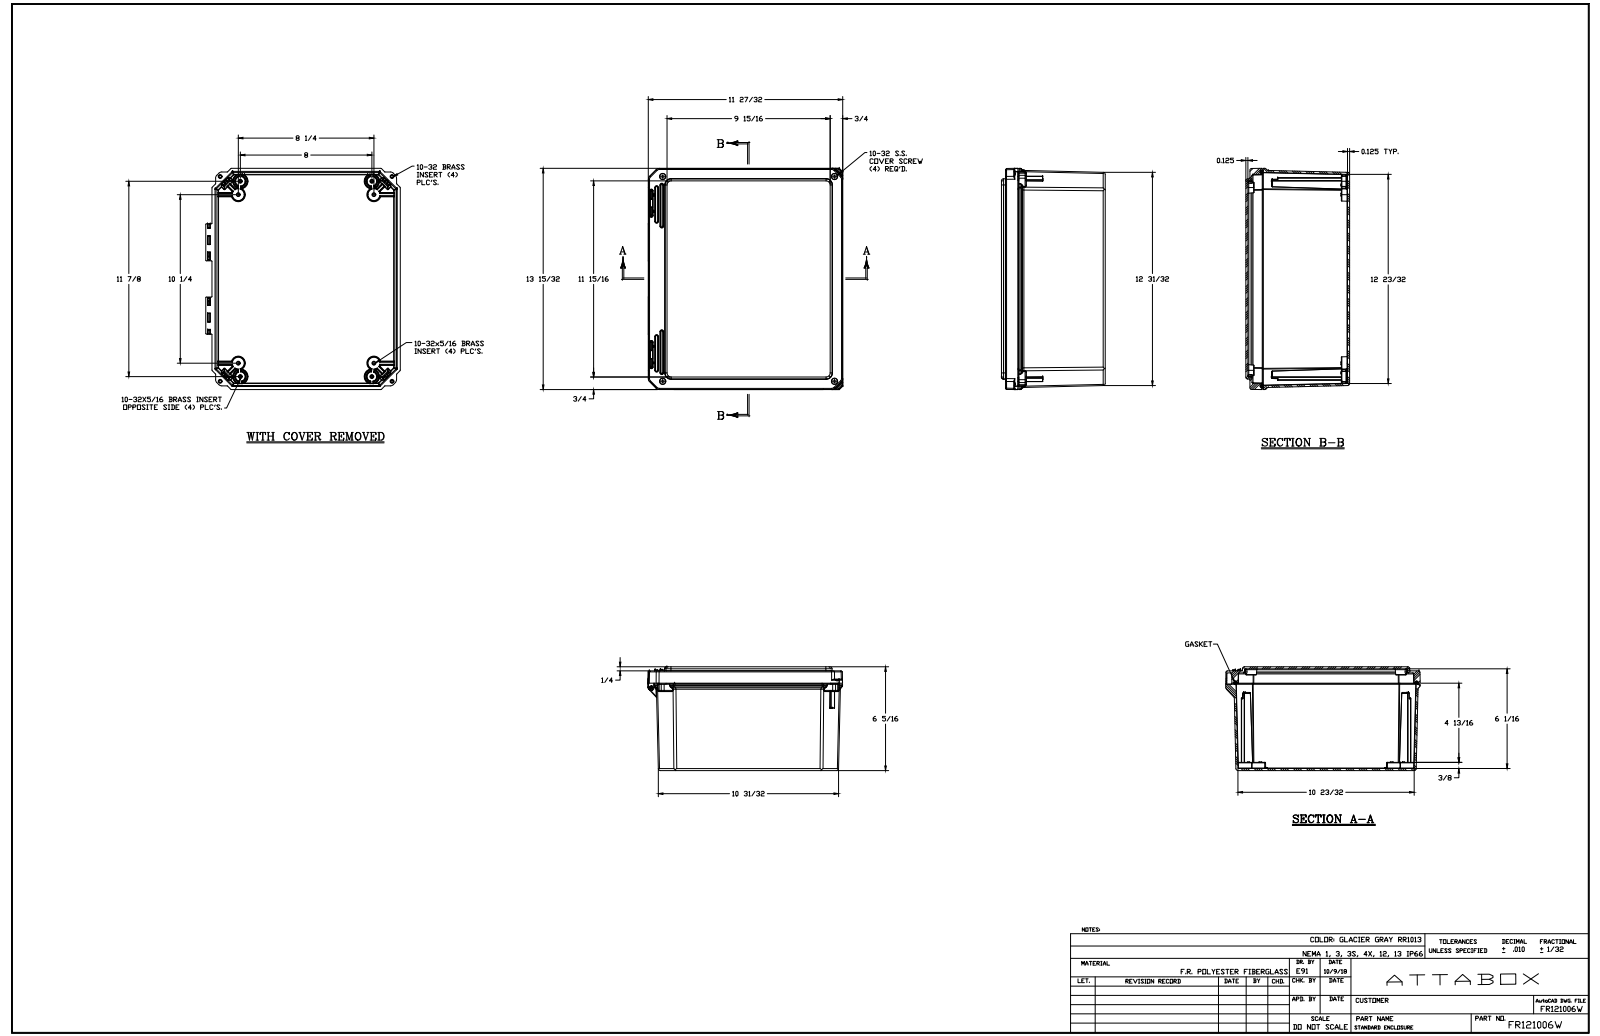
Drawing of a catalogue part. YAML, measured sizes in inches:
part_name: "FR121006W"
step_written_by: "SolidWorks 2018 (AUTOMOTIVE_DESIGN)"
units: inches
bodies: {solids: 27, faces: 2068, planar: 683, cylindrical: 758, other: 627}
overall_size: [13.46, 11.831, 6.31]
volume: 92.57
surface_area: 1268
round_holes:
  - {diameter: 0.156, count: 16}
  - {diameter: 0.152, count: 8}
  - {diameter: 0.252, count: 4}
  - {diameter: 0.253, count: 4}
  - {diameter: 0.219, count: 2}
  - {diameter: 0.227, count: 2}
  - {diameter: 0.313, count: 2}
  - {diameter: 0.137, count: 1}
round_bosses_or_shafts:
  - {diameter: 0.246, count: 16}
  - {diameter: 0.87, count: 4}
  - {diameter: 0.45, count: 4}
  - {diameter: 0.199, count: 4}
  - {diameter: 0.435, count: 2}
partial_cylinders:
  - {radius: 0.01, count: 157}
  - {radius: 0.005, count: 80}
  - {radius: 0.02, count: 57}
  - {radius: 0.03, count: 45}
  - {radius: 0.03, count: 24}
  - {radius: 0.09, count: 24}
  - {radius: 0.096, count: 24}
  - {radius: 0.125, count: 22}
face_to_face_distances: [0.125, 6.185, 6.31, 6.061, 0.139, 0.14, 0.14, 0.25, 5.935, 0.125]
hole_center_spacings: [9.417, 0.824, 1.261, 1.559, 8.165, 9.231, 11.065, 11.406]
